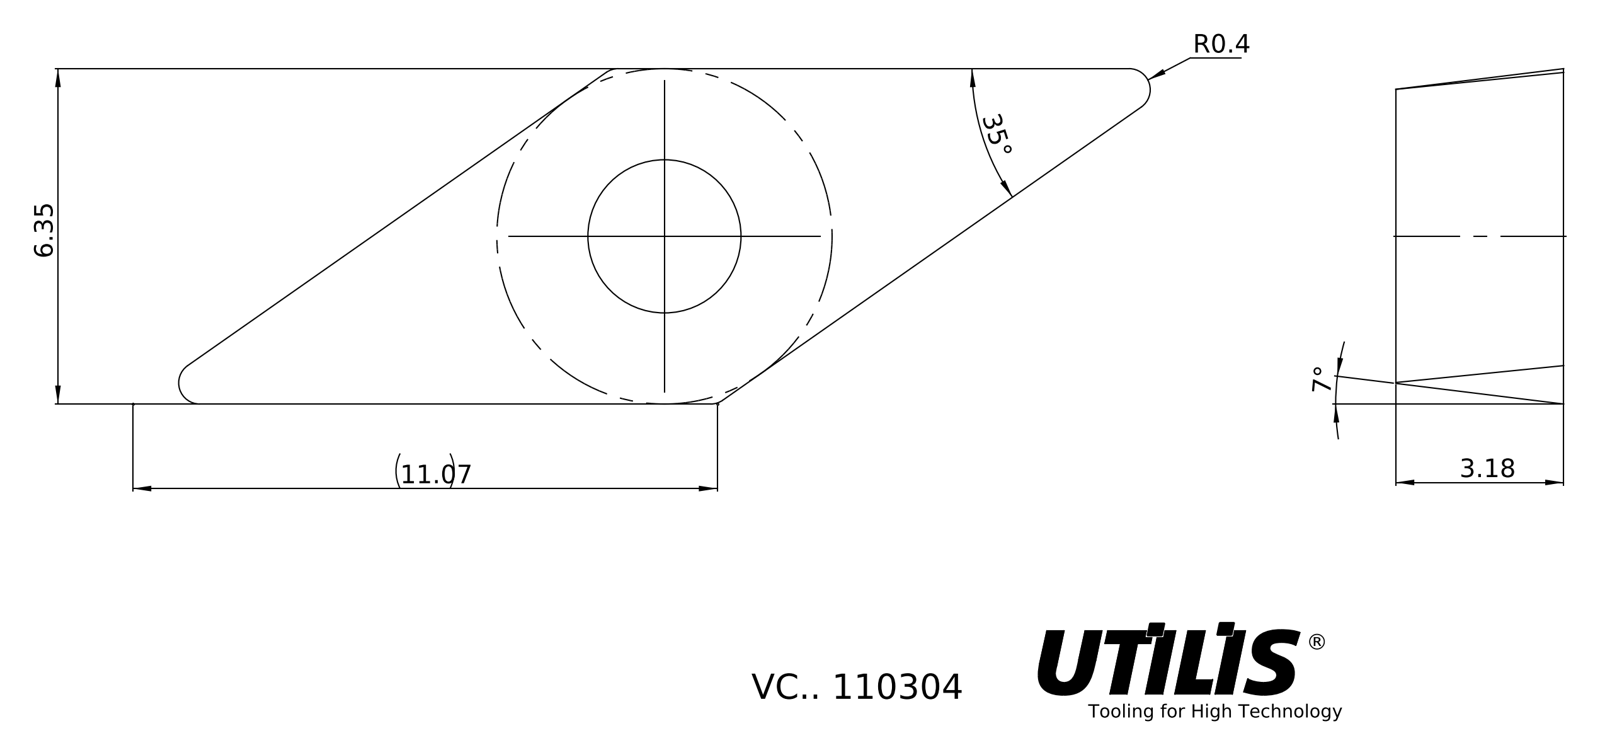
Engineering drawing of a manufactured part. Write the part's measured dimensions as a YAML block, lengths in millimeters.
part_name: "VC.. 110304"
step_written_by: "SolidWorks 2016 (AUTOMOTIVE_DESIGN)"
units: millimeters
bodies: {solids: 1, faces: 13, planar: 2, cylindrical: 2, other: 9}
overall_size: [18.4, 6.35, 3.18]
volume: 176
surface_area: 268
round_holes:
  - {diameter: 2.9, count: 1}
face_to_face_distances: [3.18]
